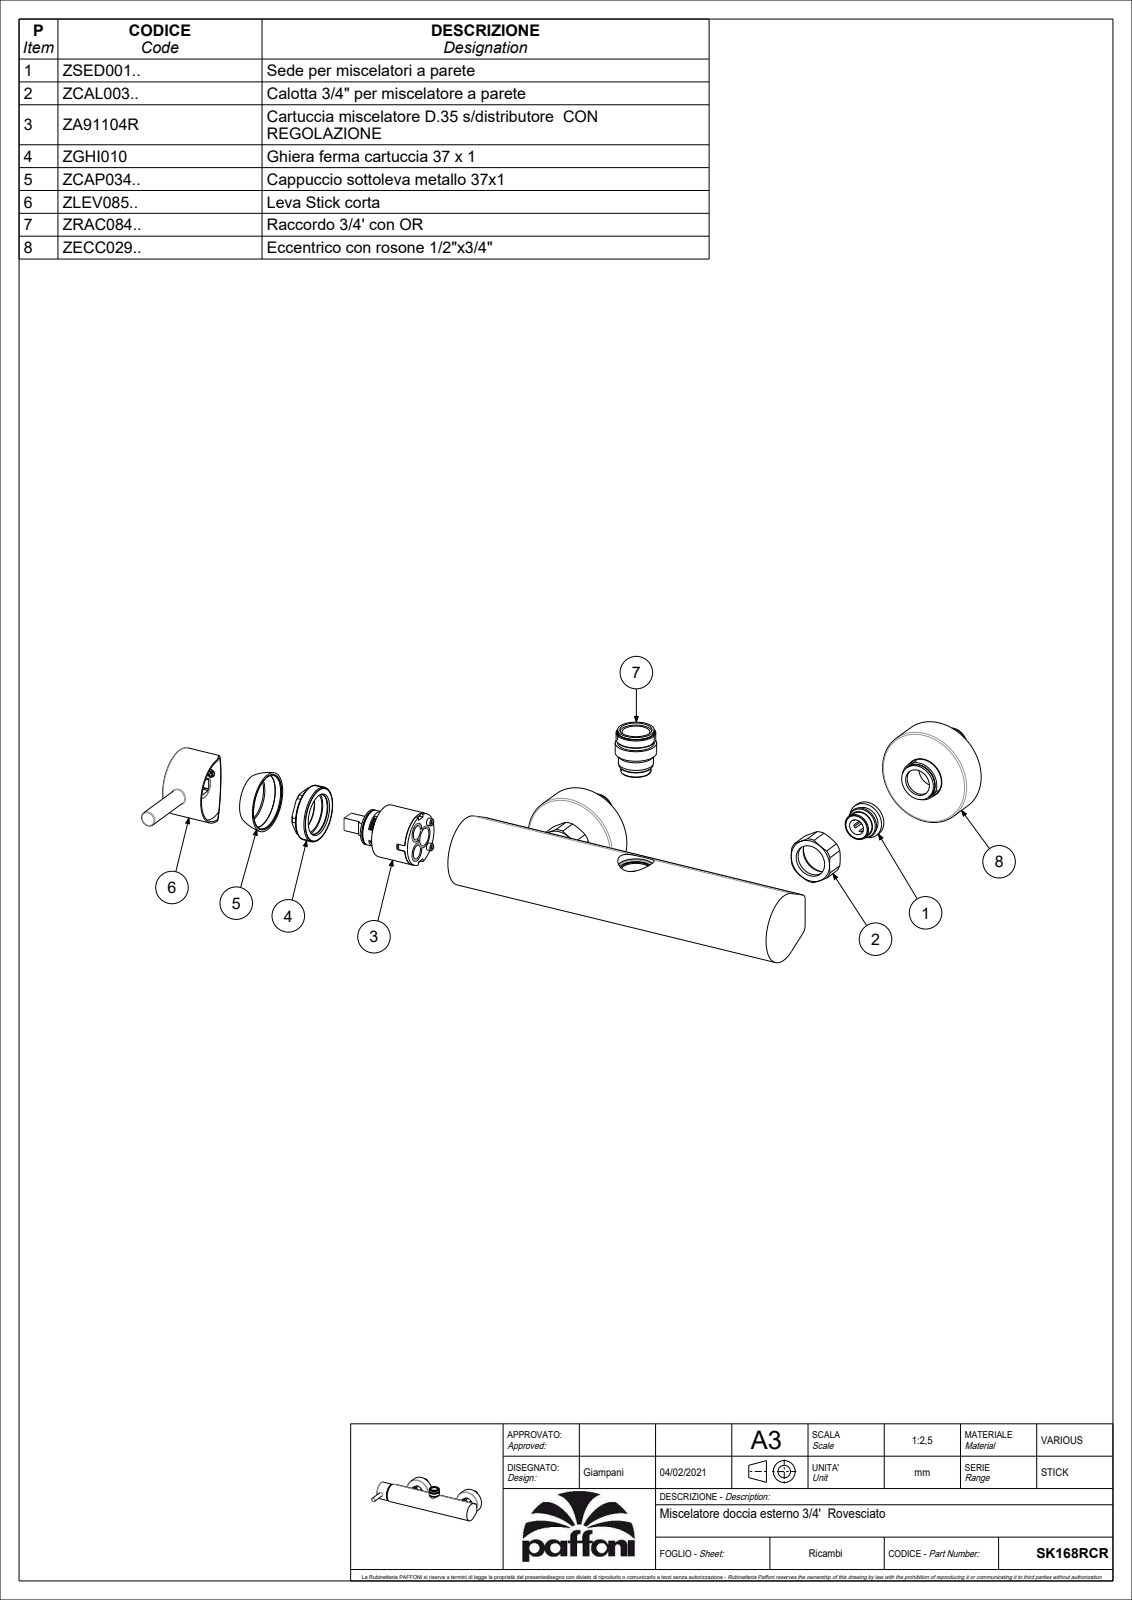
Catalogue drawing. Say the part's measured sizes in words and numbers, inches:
The part is named "SK168RCR". Its 3-D file was written by "CREO PARAMETRIC BY PTC INC, 2020044 (CONFIG_CONTROL_DESIGN)". It is 1 solid with 250 faces: 58 planar, 77 cylindrical and 115 other. Overall it measures 10.756 by 4.919 by 2.921 inches. Its volume is 39.41 cubic inches and its surface area 121.8 square inches. Round holes: 1 of diameter 0.118, 1 of diameter 0.937. Round bosses or shafts: 2 of diameter 2.5, 1 of diameter 1.752, 1 of diameter 1.071, 1 of diameter 1.024, 1 of diameter 0.945, 1 of diameter 0.906, 1 of diameter 0.394, 1 of diameter 0.299. Partial cylindrical surfaces (rounded edges, fillets, slot ends): 8 of radius 0.02, 2 of radius 0.197, 2 of radius 0.61, 2 of radius 0.728, 1 of radius 0.915. The main face-to-face distances are 0.787, 1.378, 0.591, 1.142, 1.398, 0.61, 0.02, 0.039, 0.059, 10.583.
